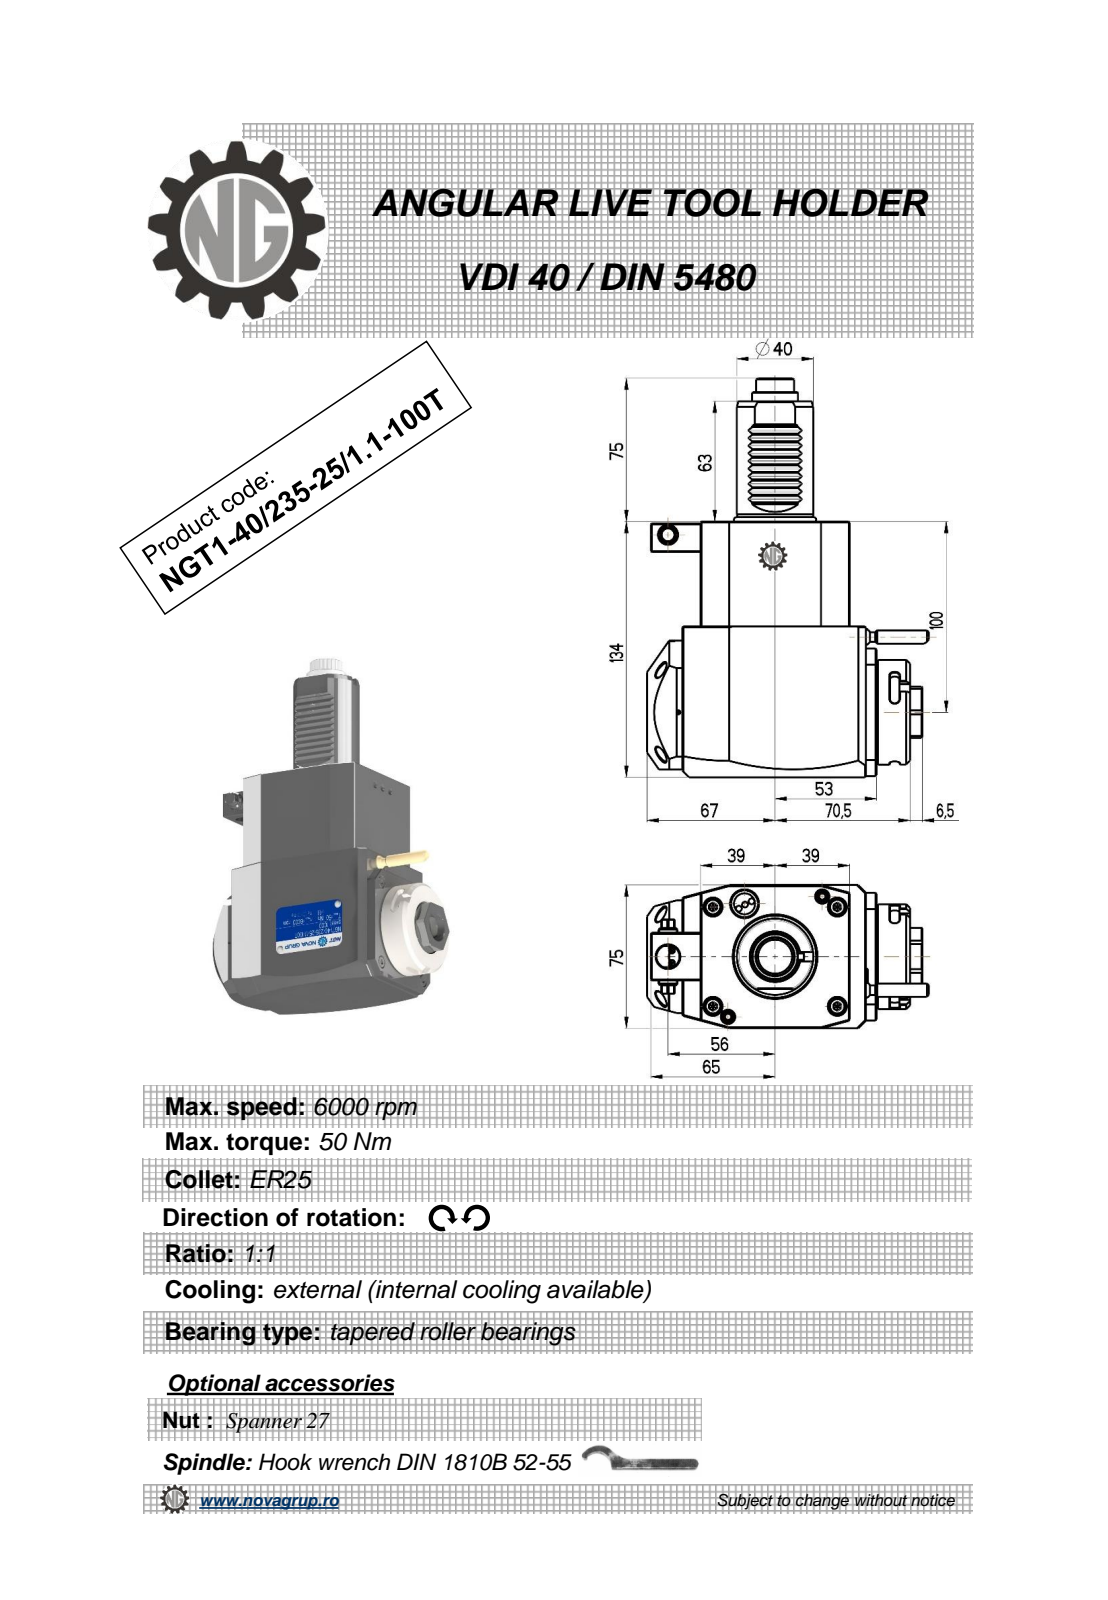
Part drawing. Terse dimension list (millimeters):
name: NGT1_40_235_25_1_1_100T
written by: PRO/ENGINEER BY PARAMETRIC TECHNOLOGY CORPORATION, 2010280 (CONFIG_CONTROL_DESIGN)
unit: mm
bodies: 1 solid, 458 faces (186 planar, 178 cylindrical, 94 other)
size: 209 × 147.33 × 75
volume: 1 074 000 mm³; area: 76 992 mm²
holes: 1× ⌀2.5, 1× ⌀3, 1× ⌀9.5, 1× ⌀12, 1× ⌀18
bosses: 2× ⌀8, 1× ⌀55, 1× ⌀48, 1× ⌀40, 1× ⌀24, 1× ⌀10, 1× ⌀7, 1× ⌀5
rounds: 48× R2.08, 10× R0.3, 6× R2.5, 2× R15, 2× R180, 1× R3.85, 1× R4.25, 1× R9.08
face distances: 75, 134, 78, 14, 92, 17.5, 31.5, 79, 84.88, 109.5
hole spacings: 43.2, 54.87, 91.5
